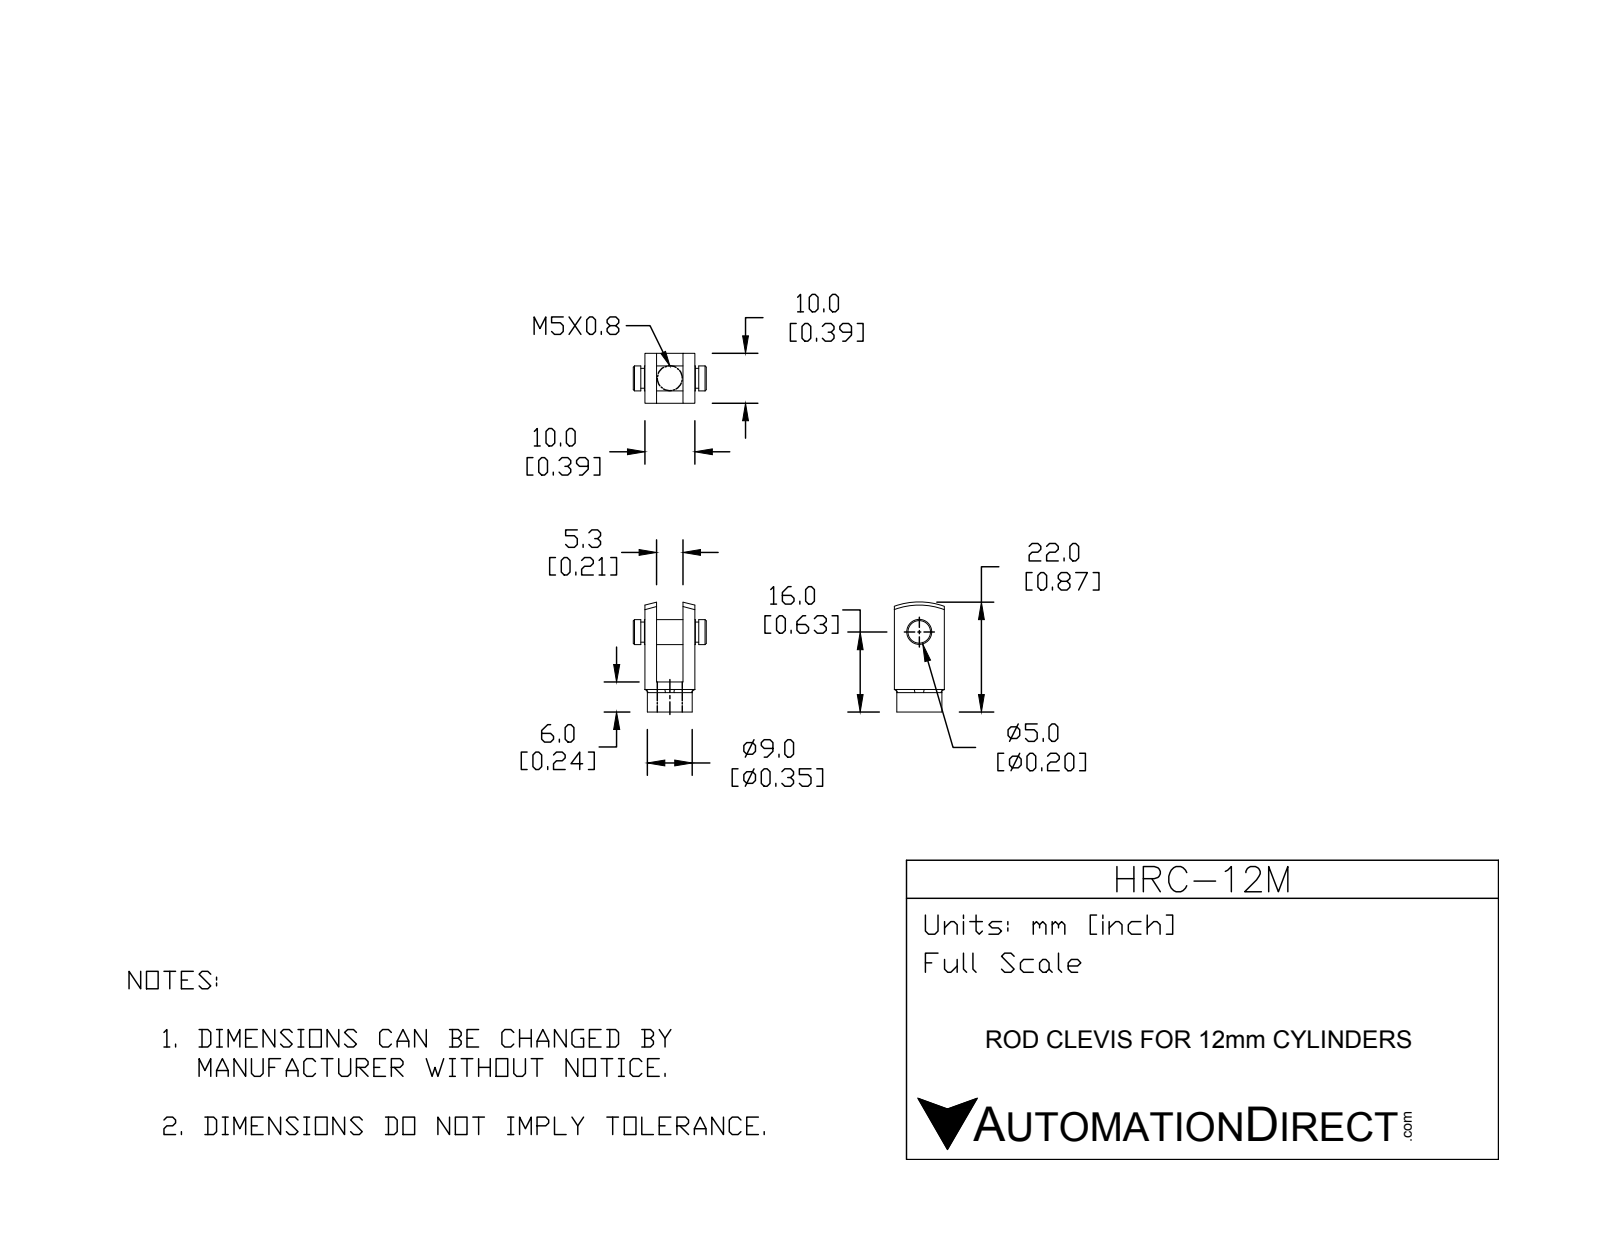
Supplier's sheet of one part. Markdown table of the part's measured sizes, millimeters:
| quantity | value |
| --- | --- |
| part name | HRC-12M |
| STEP written by | SolidWorks 2015 (CONFIG_CONTROL_DESIGN) |
| units | millimeters |
| bodies | 2 solids, 54 faces (18 planar, 18 cylindrical, 18 other) |
| overall size | 22 × 14.6 × 10 |
| volume | 1 261 mm³ |
| surface area | 1 467 mm² |
| round holes (diameter × count) | 4.2 × 1 |
| round bosses / shafts (diameter × count) | 9 × 1, 5 × 1, 4 × 1 |
| main face-to-face distances | 2.35, 7.65, 10, 5.3, 6, 1.5, 2.3, 4.65, 9.95, 12.3 |
